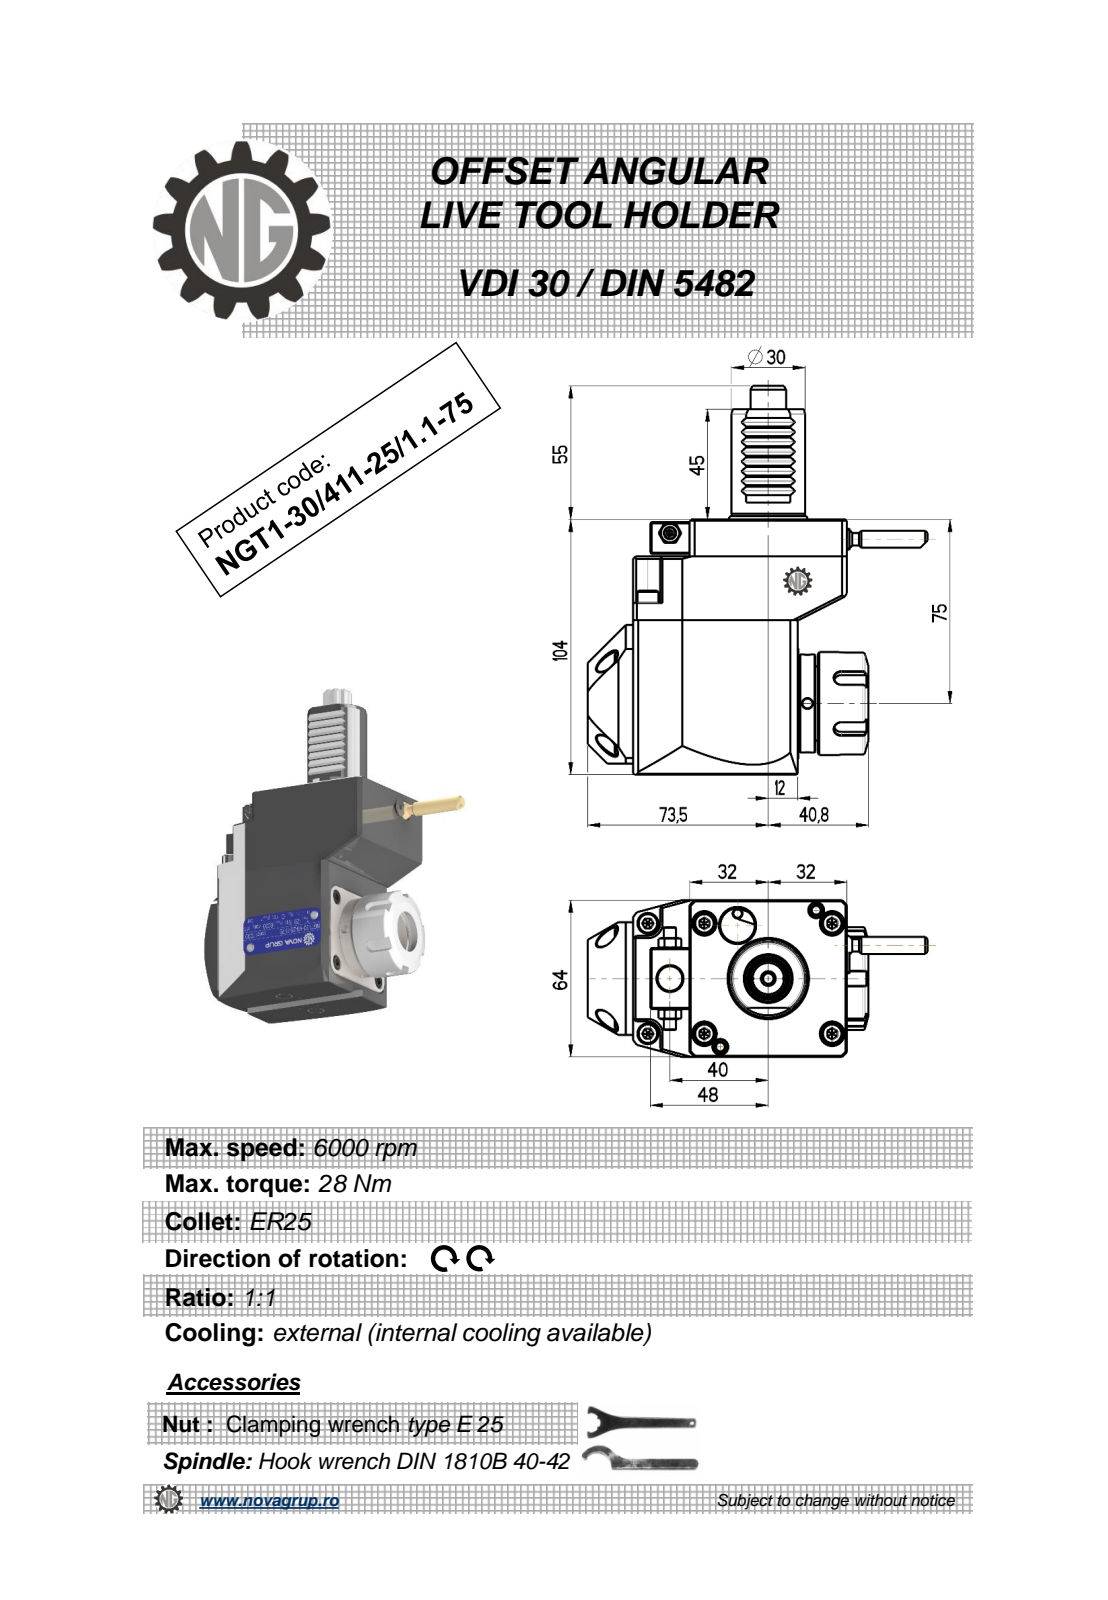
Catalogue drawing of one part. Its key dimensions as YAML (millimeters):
part_name: "NGT1_30_411_25_1_1_75"
step_written_by: "PRO/ENGINEER BY PARAMETRIC TECHNOLOGY CORPORATION, 2010280 (CONFIG_CONTROL_DESIGN)"
units: millimeters
bodies: {solids: 1, faces: 469, planar: 194, cylindrical: 118, other: 157}
overall_size: [159, 135.88, 65.4]
volume: 553568
surface_area: 53064
round_holes:
  - {diameter: 4, count: 2}
  - {diameter: 4.2, count: 2}
  - {diameter: 2.5, count: 1}
  - {diameter: 3, count: 1}
  - {diameter: 9.5, count: 1}
  - {diameter: 10, count: 1}
  - {diameter: 20.3, count: 1}
round_bosses_or_shafts:
  - {diameter: 8.96, count: 2}
  - {diameter: 5, count: 2}
  - {diameter: 42, count: 1}
  - {diameter: 40, count: 1}
  - {diameter: 33, count: 1}
  - {diameter: 30, count: 1}
  - {diameter: 7, count: 1}
partial_cylinders:
  - {radius: 2.81, count: 16}
  - {radius: 0.26, count: 12}
  - {radius: 0.3, count: 8}
  - {radius: 3, count: 5}
  - {radius: 3.5, count: 4}
  - {radius: 5.67, count: 1}
  - {radius: 7.25, count: 1}
  - {radius: 32, count: 1}
face_to_face_distances: [64, 104, 87, 67.2, 19.8, 20, 15, 89, 67, 7]
hole_center_spacings: [13.54, 15.95, 40, 55.95, 68, 68.35, 89.22]
